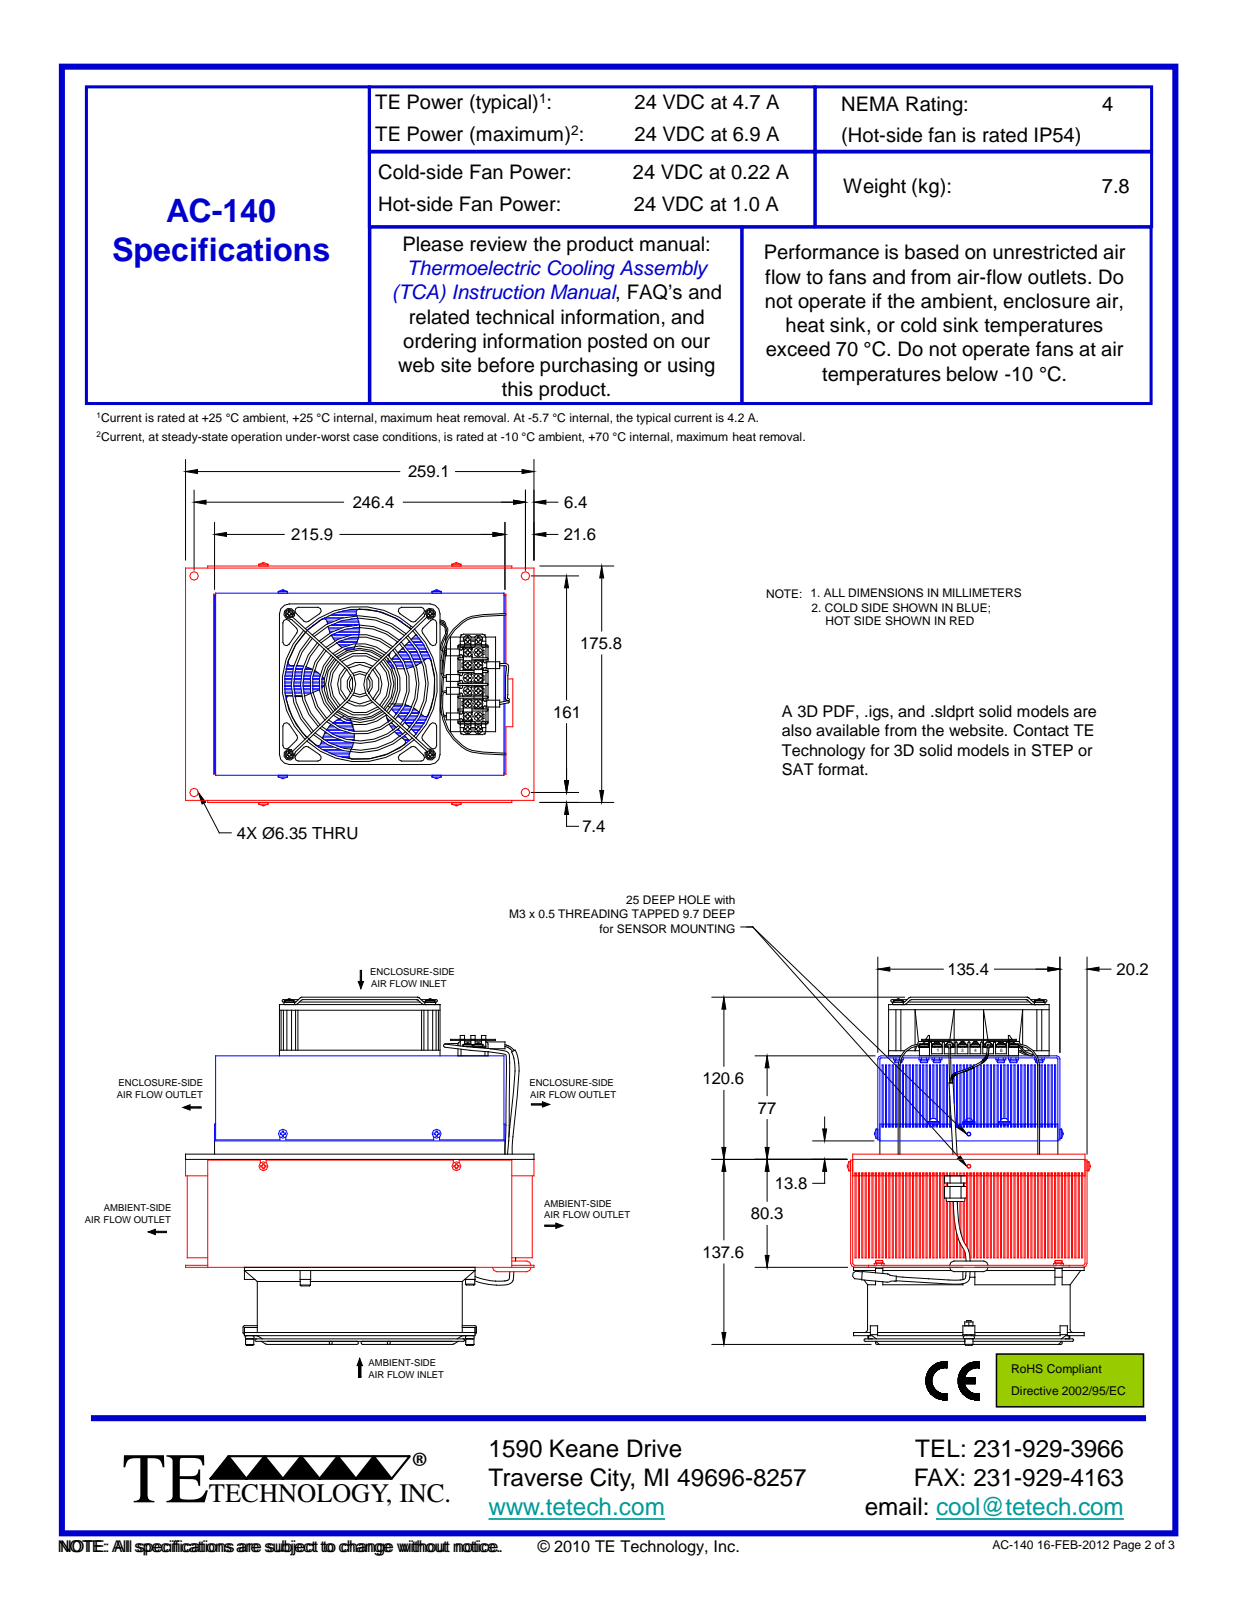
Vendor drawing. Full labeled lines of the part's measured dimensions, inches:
Part name (STEP PRODUCT): 825-3179-001 heat sink; 825-3183-001 cold sink assy; 820-2615-001; 810-3184-001 cold sink shroud (+8 more)
STEP written by: Alibre (CONFIG_CONTROL_DESIGN)
Units: inches
Bodies: 196 solids, 4716 faces (2783 planar, 827 cylindrical, 1106 other)
Overall size (bounding box): 10.2 × 10.119 × 7.118
Volume: 202 in³ · Surface area: 5 763 in²
Round holes (diameter × count): ⌀0.104 ×25, ⌀0.104 ×11, ⌀0.219 ×11, ⌀0.166 ×10, ⌀0.25 ×10, ⌀0.075 ×6, ⌀0.139 ×6, ⌀0.155 ×6, ⌀0.164 ×6, ⌀0.168 ×6, ⌀0.17 ×6, ⌀0.188 ×6
Round bosses / shafts (diameter × count): ⌀0.138 ×34, ⌀0.27 ×23, ⌀0.091 ×16, ⌀0.226 ×13, ⌀0.055 ×12, ⌀0.25 ×11, ⌀0.056 ×10, ⌀0.125 ×9
Partial cylindrical surfaces — rounded edges, fillets, slot ends (radius × count): R0.039 ×44, R0.02 ×29, R0.031 ×24, R0.037 ×21, R0.031 ×12, R0.032 ×12, R0.079 ×12, R0.015 ×8
Main face-to-face distances: 0.198, 0.396, 0.099, 0.297, 0.495, 0.594, 0.693, 0.099, 0.891, 0.792
Hole centre spacings: 2.08, 3.593, 2.917, 2.917, 4.125, 4.126, 2.202, 4.012
